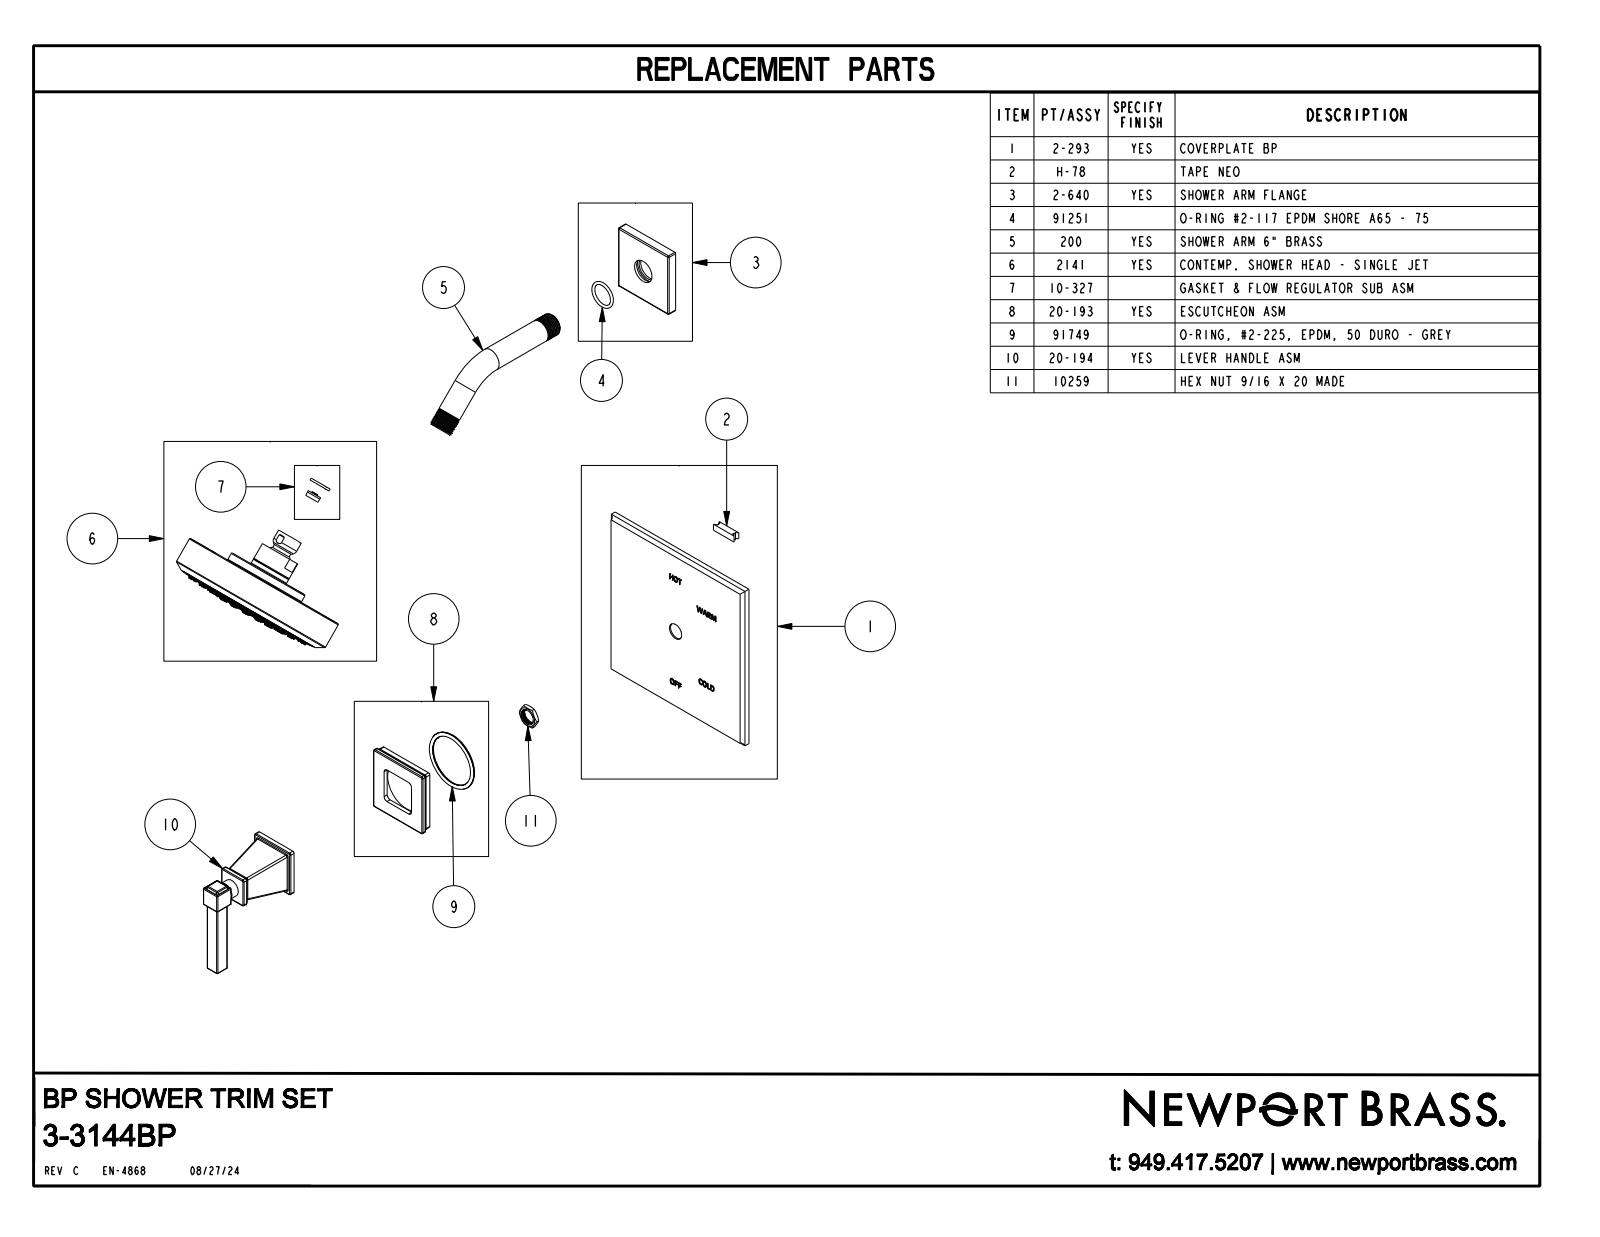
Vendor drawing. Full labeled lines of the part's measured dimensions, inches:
Part name (STEP PRODUCT): 3-3144BP
STEP written by: CREO PARAMETRIC BY PTC INC, 2018400 (CONFIG_CONTROL_DESIGN)
Units: inches
Bodies: 2 solids, 1315 faces (281 planar, 317 cylindrical, 717 other)
Overall size (bounding box): 16.475 × 8.486 × 6.5
Volume: 58.51 in³ · Surface area: 229 in²
Round holes (diameter × count): ⌀0.05 ×90, ⌀0.22 ×1, ⌀5.256 ×1
Round bosses / shafts (diameter × count): ⌀1.4 ×2, ⌀0.813 ×2, ⌀5.91 ×1, ⌀5.22 ×1, ⌀2.92 ×1, ⌀0.905 ×1, ⌀0.768 ×1, ⌀0.625 ×1
Partial cylindrical surfaces — rounded edges, fillets, slot ends (radius × count): R0.03 ×48, R0.06 ×28, R0.04 ×8, R0.09 ×8, R0.125 ×4, R0.23 ×4
Main face-to-face distances: 0.313, 0.35, 0.037, 0.291, 0.723, 0.41, 0.373, 6.5, 0.5, 3
Hole centre spacings: 0.98, 1.41, 0.43, 0.55, 1.343, 1.893, 0.574, 0.851
